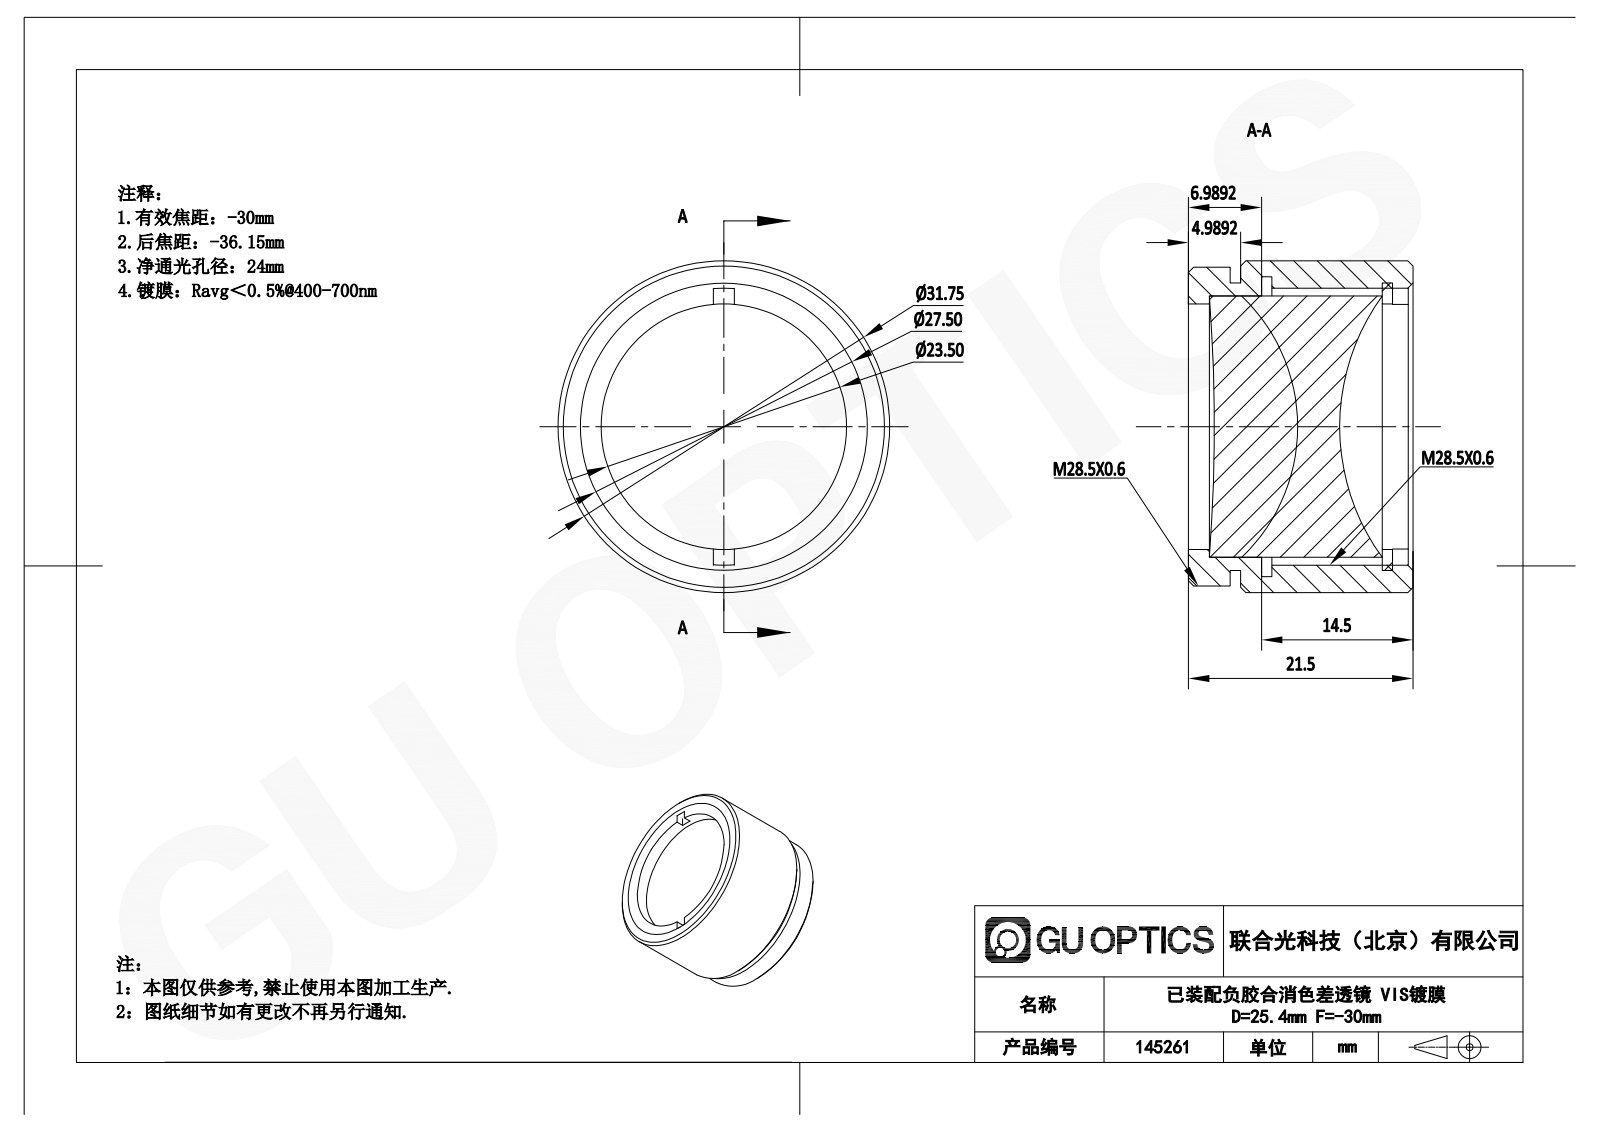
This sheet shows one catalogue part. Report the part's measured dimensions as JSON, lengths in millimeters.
{"part_name": "145261", "step_written_by": "SolidWorks 2020 (CONFIG_CONTROL_DESIGN)", "units": "millimeters", "bodies": {"solids": 4, "faces": 54, "planar": 16, "cylindrical": 22, "other": 16}, "overall_size": [31.75, 31.75, 21.5], "volume_mm3": 12479, "surface_area_mm2": 9156, "round_holes": [[23.5, 1], [26.5, 1], [28.7, 1]], "round_bosses_or_shafts": [[31.75, 1], [30.5, 1], [27.5, 1], [25, 1]], "face_to_face_distances": [3, 2, 1, 4, 5, 11.55, 18.55, 7, 21.05, 14.05]}
